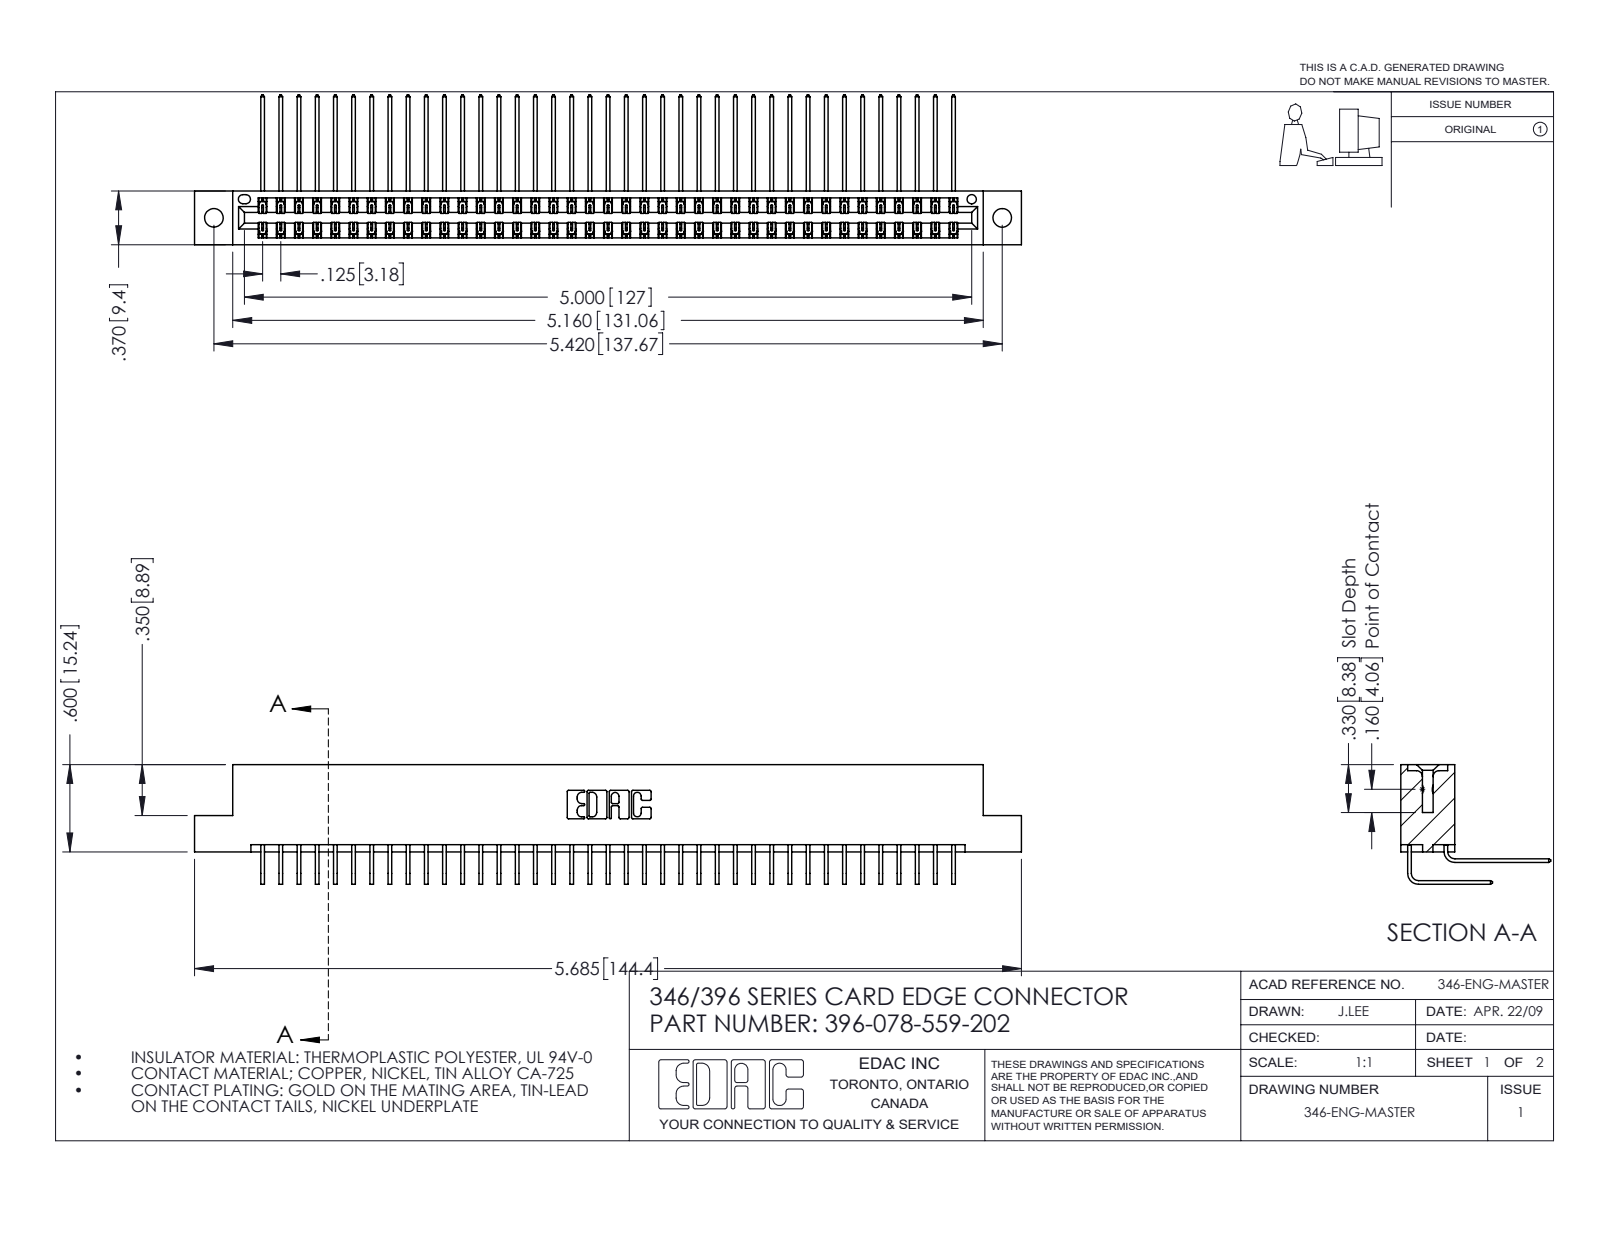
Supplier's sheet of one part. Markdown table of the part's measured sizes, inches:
| quantity | value |
| --- | --- |
| part name | 346 Part_Flush Mounting Lugs - 0.128 Dia; 396-078-559-202; 345-292-001_559 Tail - 2; 345-292-001_558 559 Tail - 1 |
| STEP written by | SolidWorks 2016 (CONFIG_CONTROL_DESIGN) |
| units | inches |
| bodies | 79 solids, 4334 faces (2962 planar, 1372 cylindrical, 0 other) |
| overall size | 5.685 × 1.03 × 0.823 |
| volume | 0.883 in³ |
| surface area | 33.69 in² |
| round holes (diameter × count) | 0.128 × 2, 0.064 × 1 |
| partial cylindrical surfaces (radius × count) | 0.006 × 117, 0.01 × 22, 0.007 × 6, 0.031 × 6, 0.026 × 3, 0.014 × 2, 0.022 × 2, 0.024 × 2 |
| main face-to-face distances | 0.048, 0.322, 0.025, 0.37, 0.25, 0.072, 0.298, 0.275, 0.148, 0.222 |
| hole center spacings | 0.246, 5.211, 5.42 |
